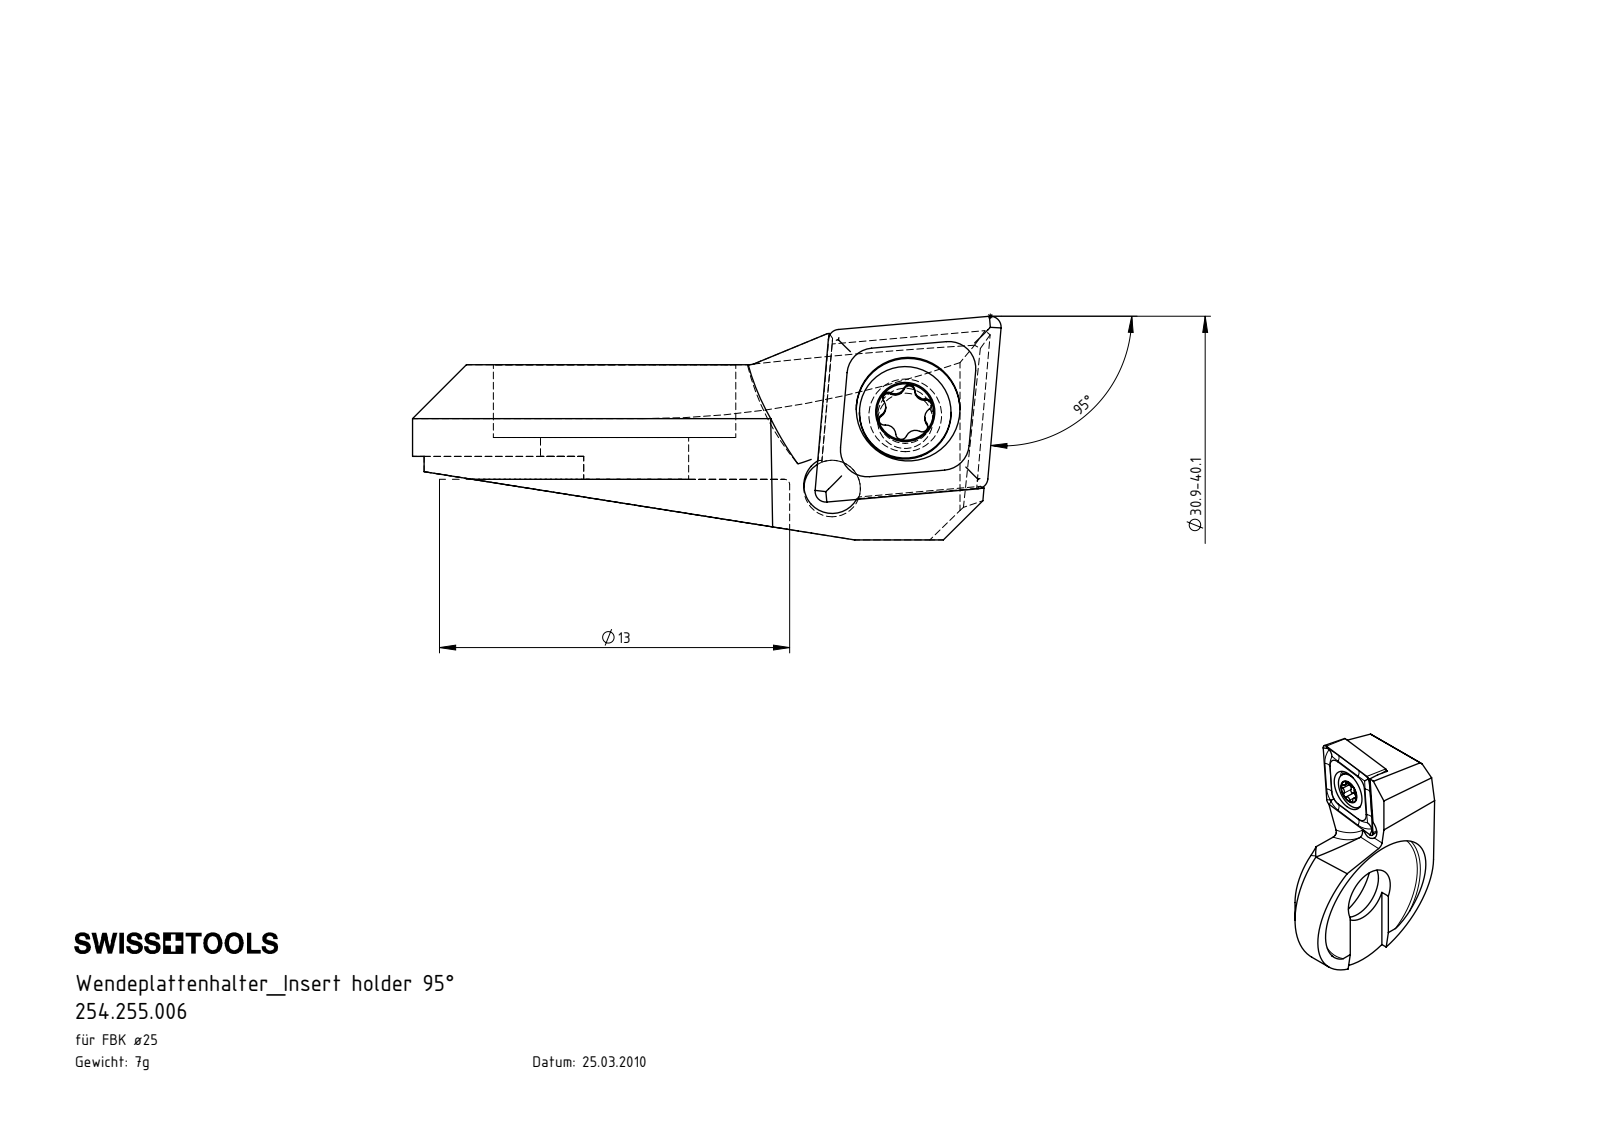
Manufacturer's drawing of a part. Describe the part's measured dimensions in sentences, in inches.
The part is named "WCA-ER2.001.006_A; F25-WCA.002.006; CCMT060204; F25-WCA.002.006_C_fertigbearbeitet". Its 3-D file was written by "SolidWorks 2015 (CONFIG_CONTROL_DESIGN)". It is 5 solids with 143 faces: 49 planar, 43 cylindrical and 51 other. Overall it measures 0.86 by 0.591 by 0.327 inches. Its volume is 0.053 cubic inches and its surface area 2.029 square inches. Round holes: 1 of diameter 0.081, 1 of diameter 0.083, 1 of diameter 0.11, 1 of diameter 0.152, 1 of diameter 0.217, 1 of diameter 0.354. Round bosses or shafts: 1 of diameter 0.134, 1 of diameter 0.098. Partial cylindrical surfaces (rounded edges, fillets, slot ends): 6 of radius 0.008, 5 of radius 0.014, 2 of radius 0.02, 1 of radius 0.014, 1 of radius 0.041, 1 of radius 0.256, 1 of radius 0.295, 1 of radius 0.354. The main face-to-face distances are 0.167, 0.163, 0.089, 0.106, 0.102, 0.061, 0.09, 0.134, 0.13, 0.028. The hole center spacings are 0.151, 0.157.
